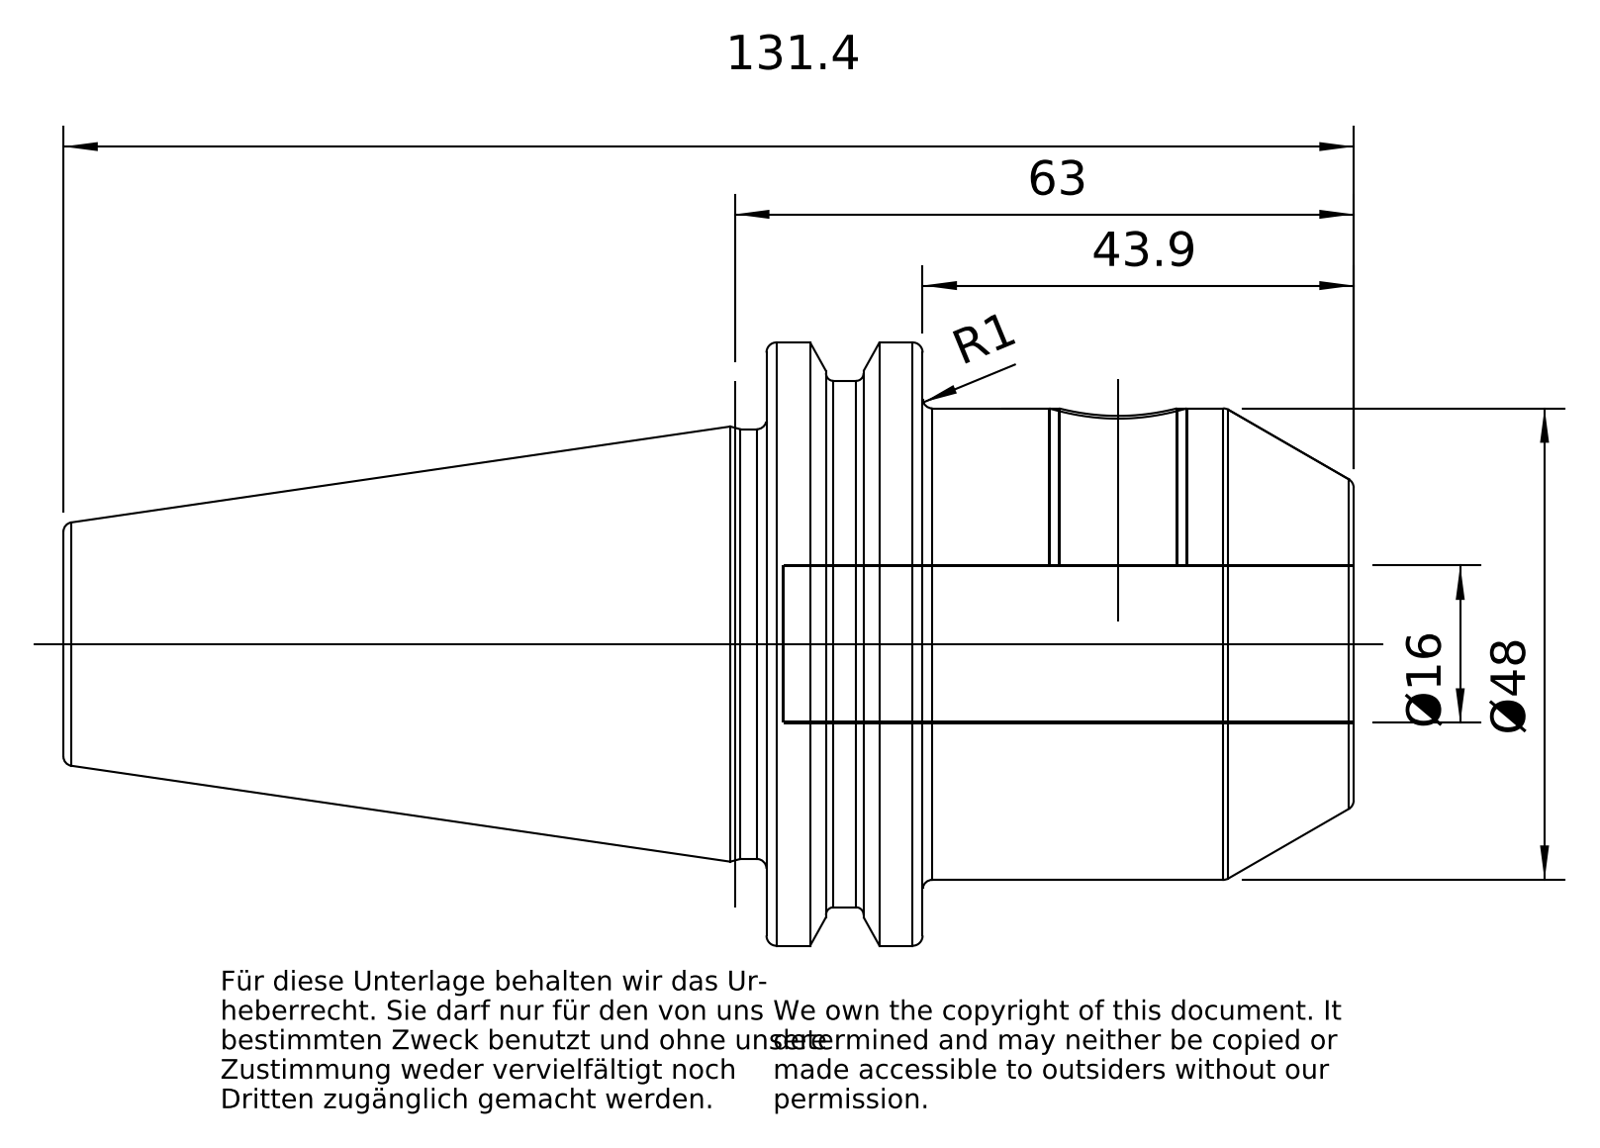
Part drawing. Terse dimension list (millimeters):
name: 40-300-16
written by: PRO/ENGINEER BY PARAMETRIC TECHNOLOGY CORPORATION, 2010430 (CONFIG_CONTROL_DESIGN)
unit: mm
bodies: 1 solid, 100 faces (23 planar, 28 cylindrical, 49 other)
size: 131.25 × 63.52 × 61.42
volume: 165 149 mm³; area: 29 635 mm²
holes: 1× ⌀12, 1× ⌀13.84, 1× ⌀14, 1× ⌀16, 1× ⌀17.01, 1× ⌀17.5
bosses: 1× ⌀48, 1× ⌀43.75, 1× ⌀16.01
rounds: 1× R1.35, 1× R28, 1× R31.76
face distances: 15.85, 59.8, 43.95, 47.4, 1.7, 14.15, 58.1, 16.2, 71.45, 73.15
